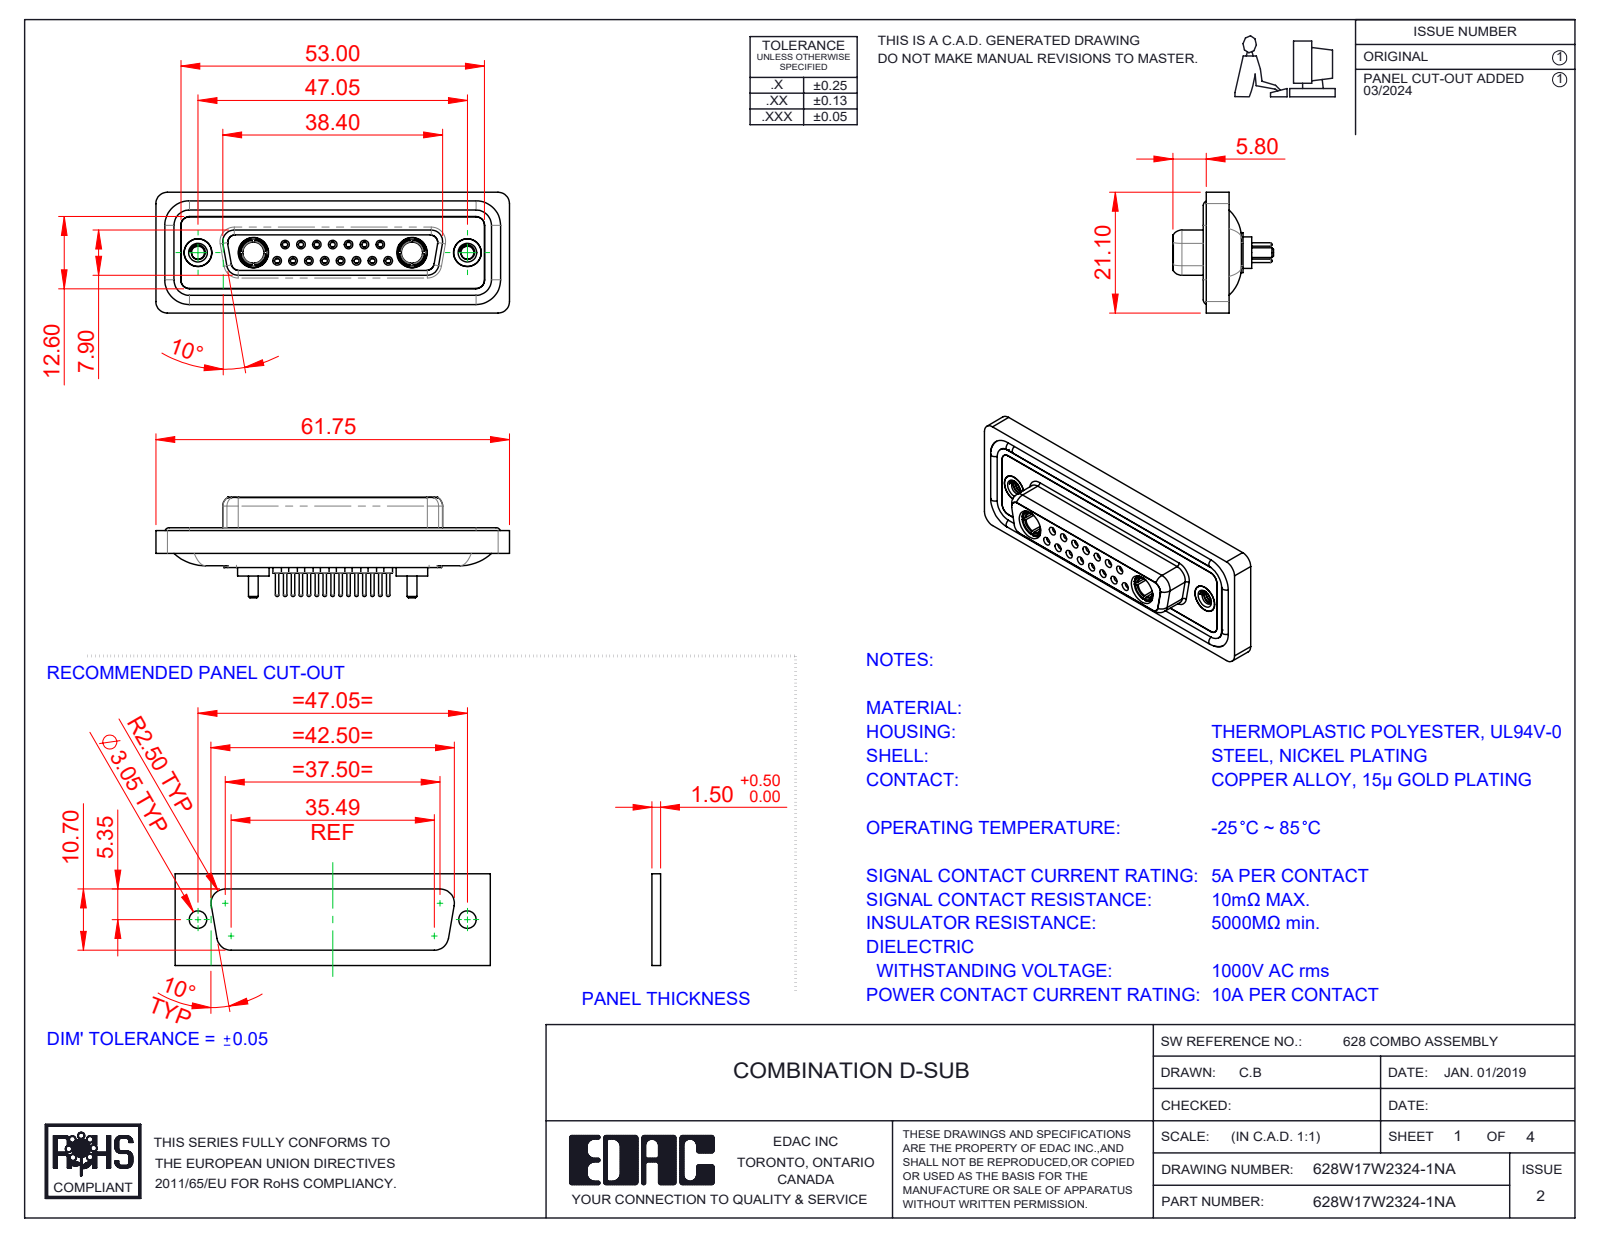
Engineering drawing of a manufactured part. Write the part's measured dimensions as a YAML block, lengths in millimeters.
part_name: "628Combo Threaded Rivet_A; 628Combo Shell Front_25 Contacts; 628Combo Shell Rear_25 Contacts; 628Combo Waterproof Housing_25 Contacts (+5 more)"
step_written_by: "SolidWorks 2023 (CONFIG_CONTROL_DESIGN)"
units: millimeters
bodies: {solids: 26, faces: 1357, planar: 388, cylindrical: 521, other: 448}
overall_size: [61.75, 21.1, 17.55]
volume: 8296
surface_area: 13828
round_holes:
  - {diameter: 0.9, count: 15}
  - {diameter: 1.1, count: 15}
  - {diameter: 1.5, count: 15}
  - {diameter: 2, count: 15}
  - {diameter: 1.6, count: 8}
  - {diameter: 1.7, count: 7}
  - {diameter: 4.85, count: 4}
  - {diameter: 2.26, count: 2}
  - {diameter: 3.7, count: 2}
  - {diameter: 4, count: 2}
  - {diameter: 4.05, count: 2}
  - {diameter: 5, count: 2}
round_bosses_or_shafts:
  - {diameter: 2.2, count: 15}
  - {diameter: 0.6, count: 15}
  - {diameter: 1.6, count: 11}
  - {diameter: 5.5, count: 2}
  - {diameter: 5.2, count: 2}
  - {diameter: 4.96, count: 2}
  - {diameter: 4.95, count: 2}
  - {diameter: 4.8, count: 2}
partial_cylinders:
  - {radius: 1.5, count: 22}
  - {radius: 2, count: 18}
  - {radius: 1.35, count: 8}
  - {radius: 1.6, count: 8}
  - {radius: 0.25, count: 4}
  - {radius: 0.5, count: 4}
  - {radius: 0.6, count: 4}
  - {radius: 0.65, count: 4}
face_to_face_distances: [0.4, 1.8, 7.45, 5.65, 6.6, 0.5, 7.05, 1.6, 2.9, 1.1]
hole_center_spacings: [3.16, 2.77, 8.31, 5.54, 5.03, 5.04, 7.49, 11.08]
